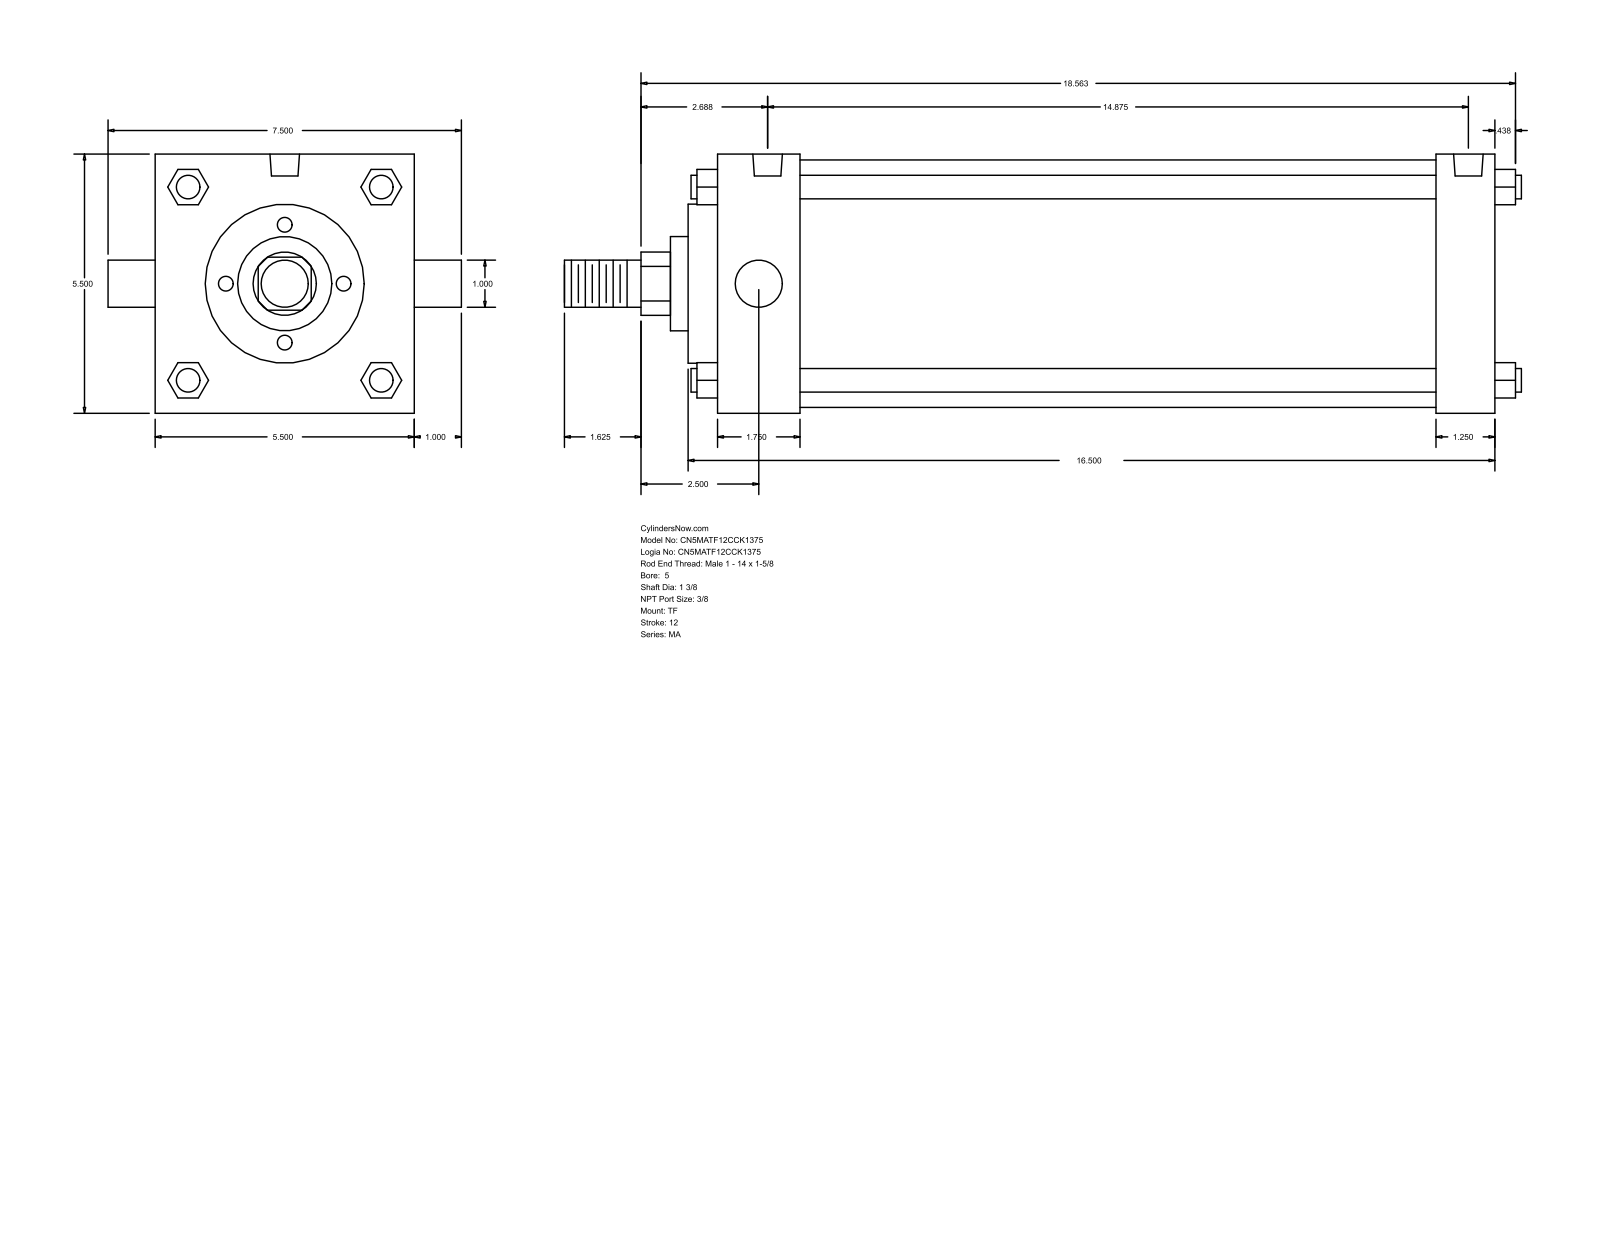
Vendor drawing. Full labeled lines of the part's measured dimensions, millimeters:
Part name (STEP PRODUCT): MA_TF__0500_1.375
STEP written by: GSSL Pune (CONFIG_CONTROL_DESIGN)
Units: millimetres
Bodies: 0 solids, 122 faces (93 planar, 29 cylindrical, 0 other)
Overall size (bounding box): 515.94 × 190.5 × 139.7
Round holes (diameter × count): ⌀11.11 ×3, ⌀15.93 ×2
Round bosses / shafts (diameter × count): ⌀12.7 ×4, ⌀25.4 ×2, ⌀133.35 ×1, ⌀85.72 ×1, ⌀50.8 ×1, ⌀34.92 ×1
Partial cylindrical surfaces — rounded edges, fillets, slot ends (radius × count): R17.06 ×1
Main face-to-face distances: 139.7, 419.11, 387.35, 31.76, 44.45, 342.9, 374.66, 15.87, 60.32, 403.22
Hole centre spacings: 4.77, 373.06, 368.29, 377.83
